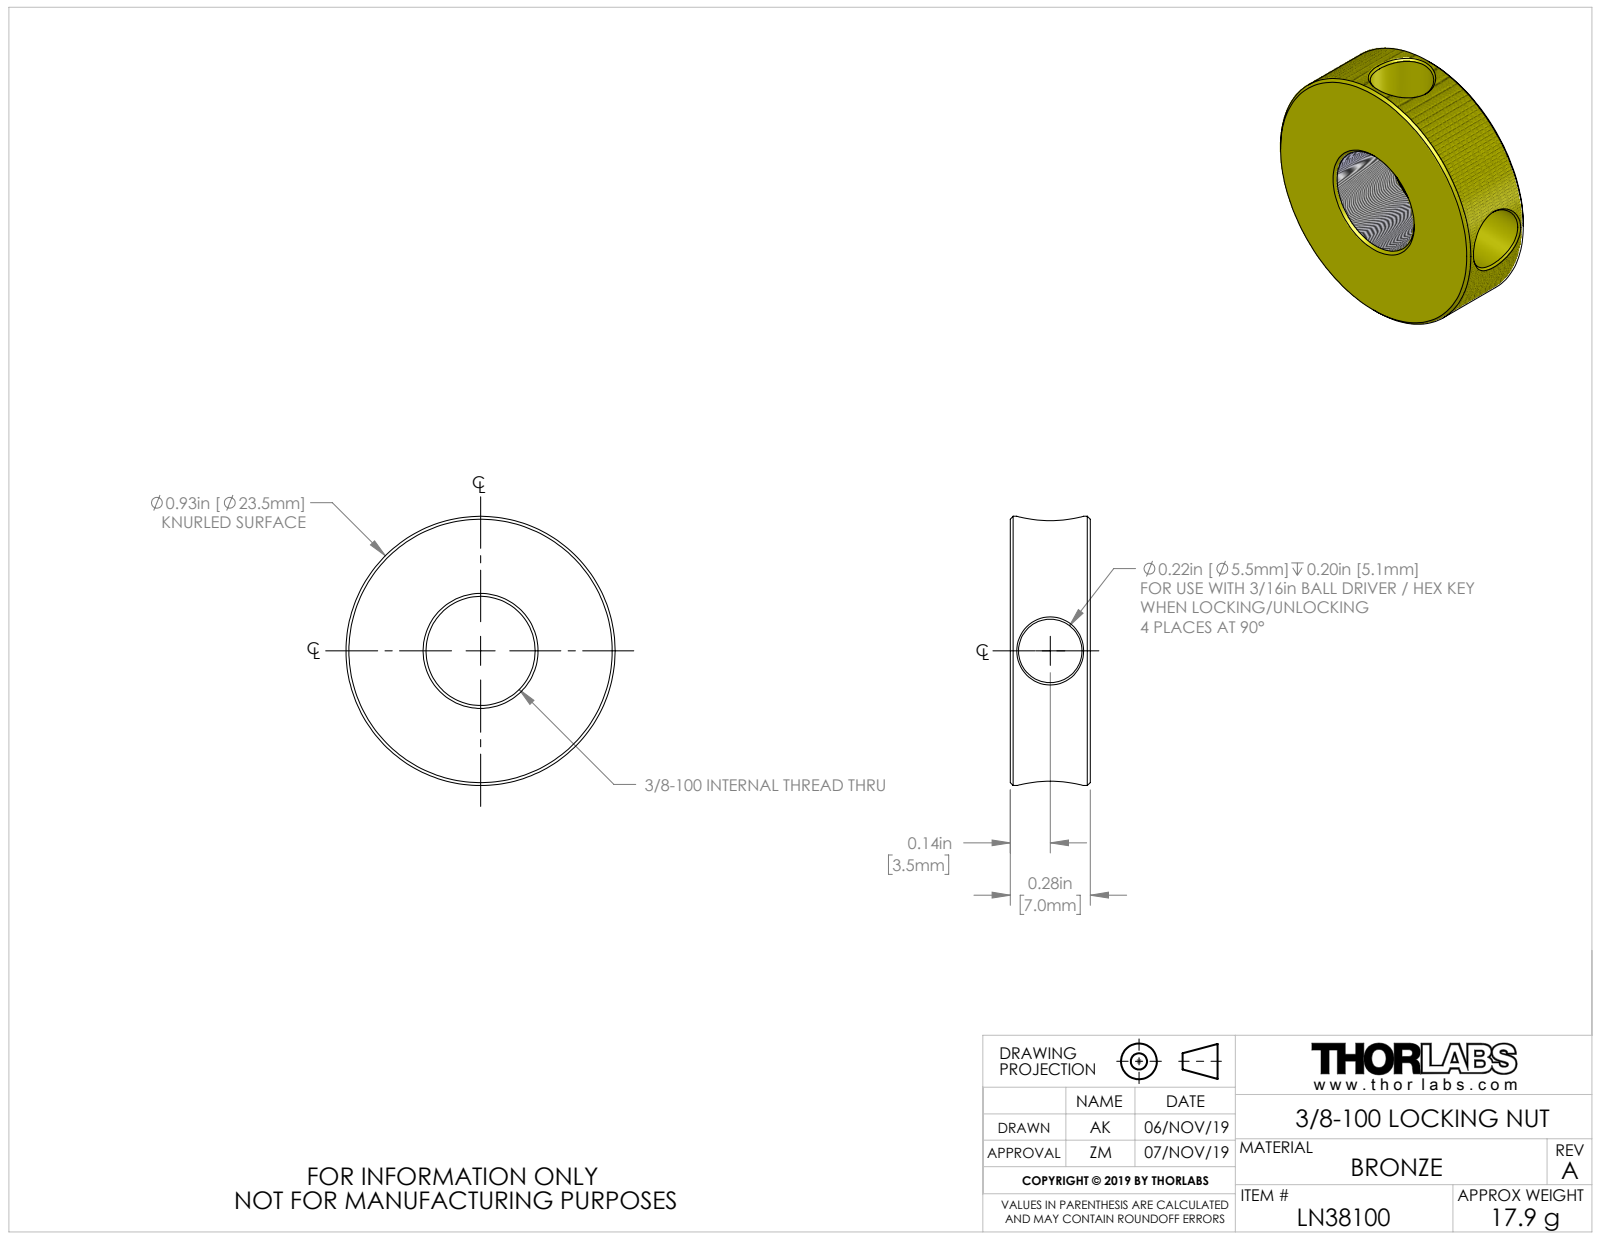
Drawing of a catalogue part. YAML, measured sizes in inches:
part_name: "TTN200026-E0W"
step_written_by: "SolidWorks 2018 (AUTOMOTIVE_DESIGN)"
units: inches
bodies: {solids: 1, faces: 34, planar: 6, cylindrical: 12, other: 16}
overall_size: [0.925, 0.925, 0.275]
volume: 0.125
surface_area: 2.713
round_holes:
  - {diameter: 0.218, count: 2}
  - {diameter: 0.375, count: 1}
round_bosses_or_shafts:
  - {diameter: 0.925, count: 1}
face_to_face_distances: [0.275, 0.525, 0.525]
